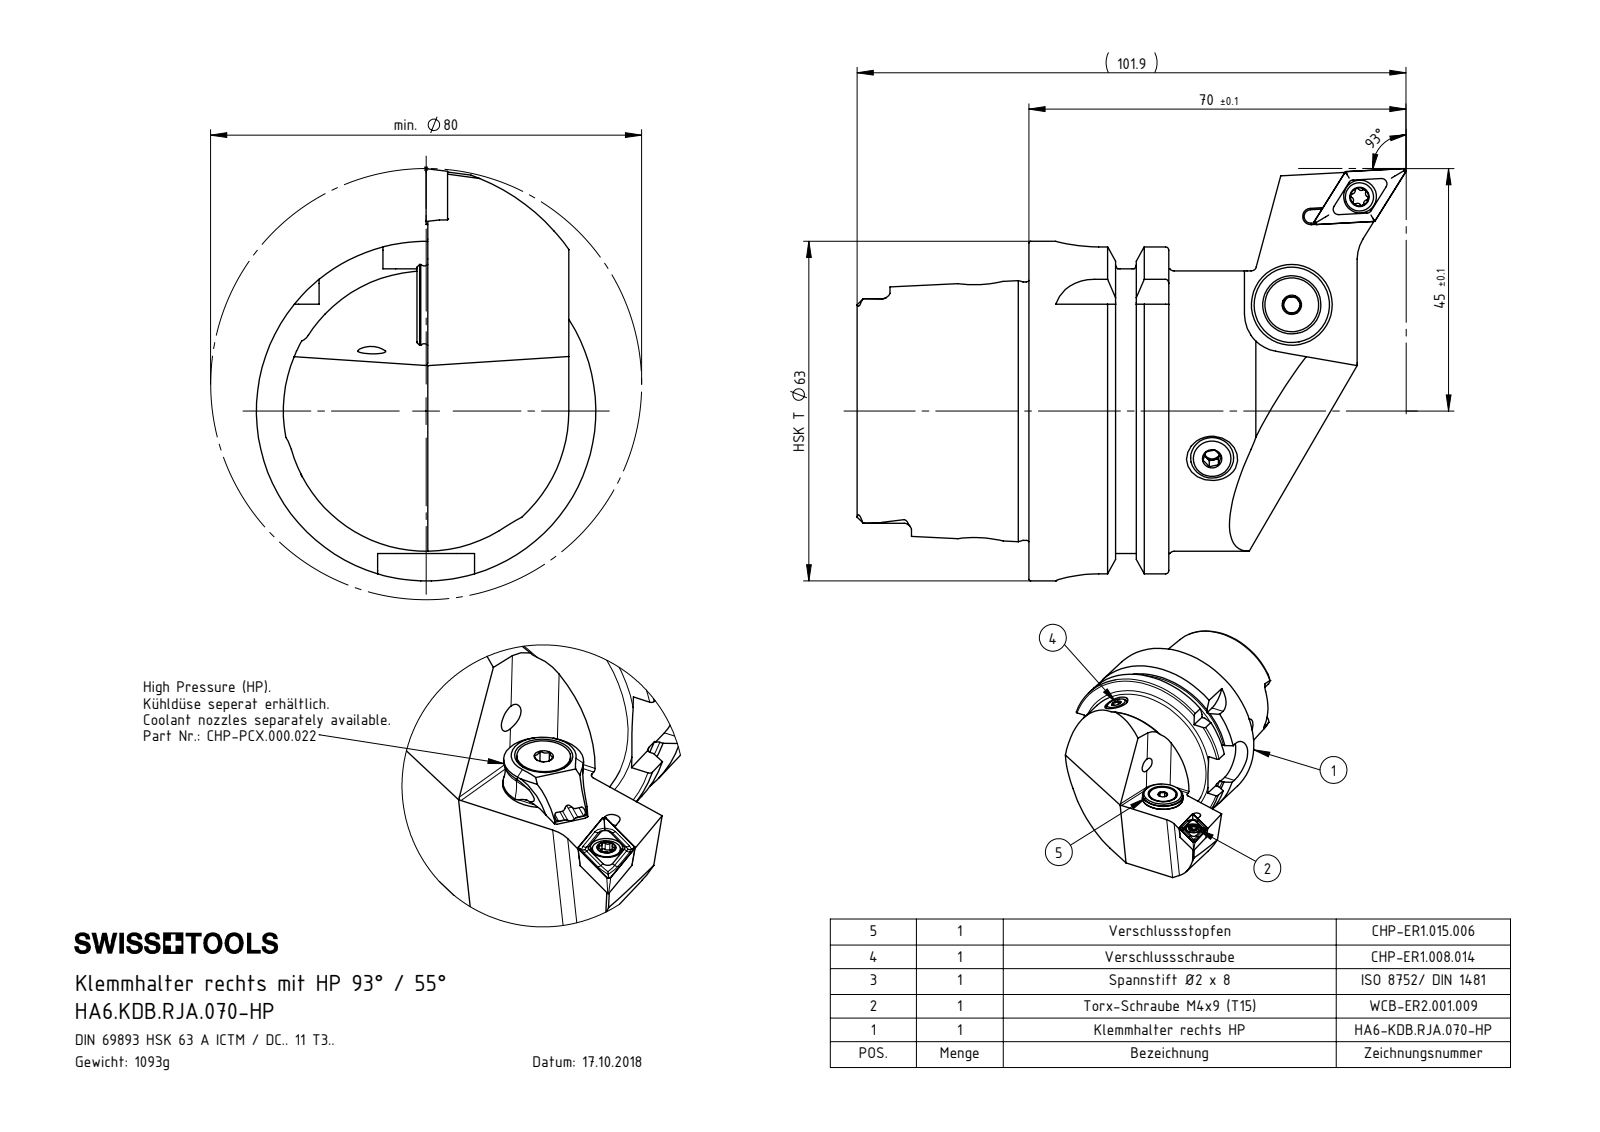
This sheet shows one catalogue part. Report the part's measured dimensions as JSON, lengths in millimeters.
{"part_name": "DIN 7991 - M5x15; WCB-ER2.001.009_A; DIN 3771 - 13x1; CHP-ER1.015.006_A (+6 more)", "step_written_by": "SolidWorks 2017 (AUTOMOTIVE_DESIGN)", "units": "millimeters", "bodies": {"solids": 8, "faces": 416, "planar": 119, "cylindrical": 120, "other": 177}, "overall_size": [101.91, 76.5, 63], "volume_mm3": 138815, "surface_area_mm2": 32486, "round_holes": [[4.2, 2], [5, 2], [1.2, 1], [2, 1], [2.5, 1], [3, 1], [3.3, 1], [4.4, 1], [5.2, 1], [6.1, 1], [7, 1], [7.5, 1]], "round_bosses_or_shafts": [[63, 1], [54.95, 1], [52, 1], [47.94, 1], [15, 1], [13.4, 1], [10, 1], [8, 1]], "partial_cylinders_radius": [[0.34, 6], [0.59, 6], [1.4, 6], [8, 4], [0.5, 2], [2.82, 2], [2.88, 2], [7, 2]], "face_to_face_distances": [25.95, 16, 9.95, 26.2, 31.9, 41.85, 57.85, 52.8, 21.8, 11.85], "hole_center_spacings": [4.5, 20.82, 20.92, 23.63, 23.74, 46.21, 50.59, 67.33]}
